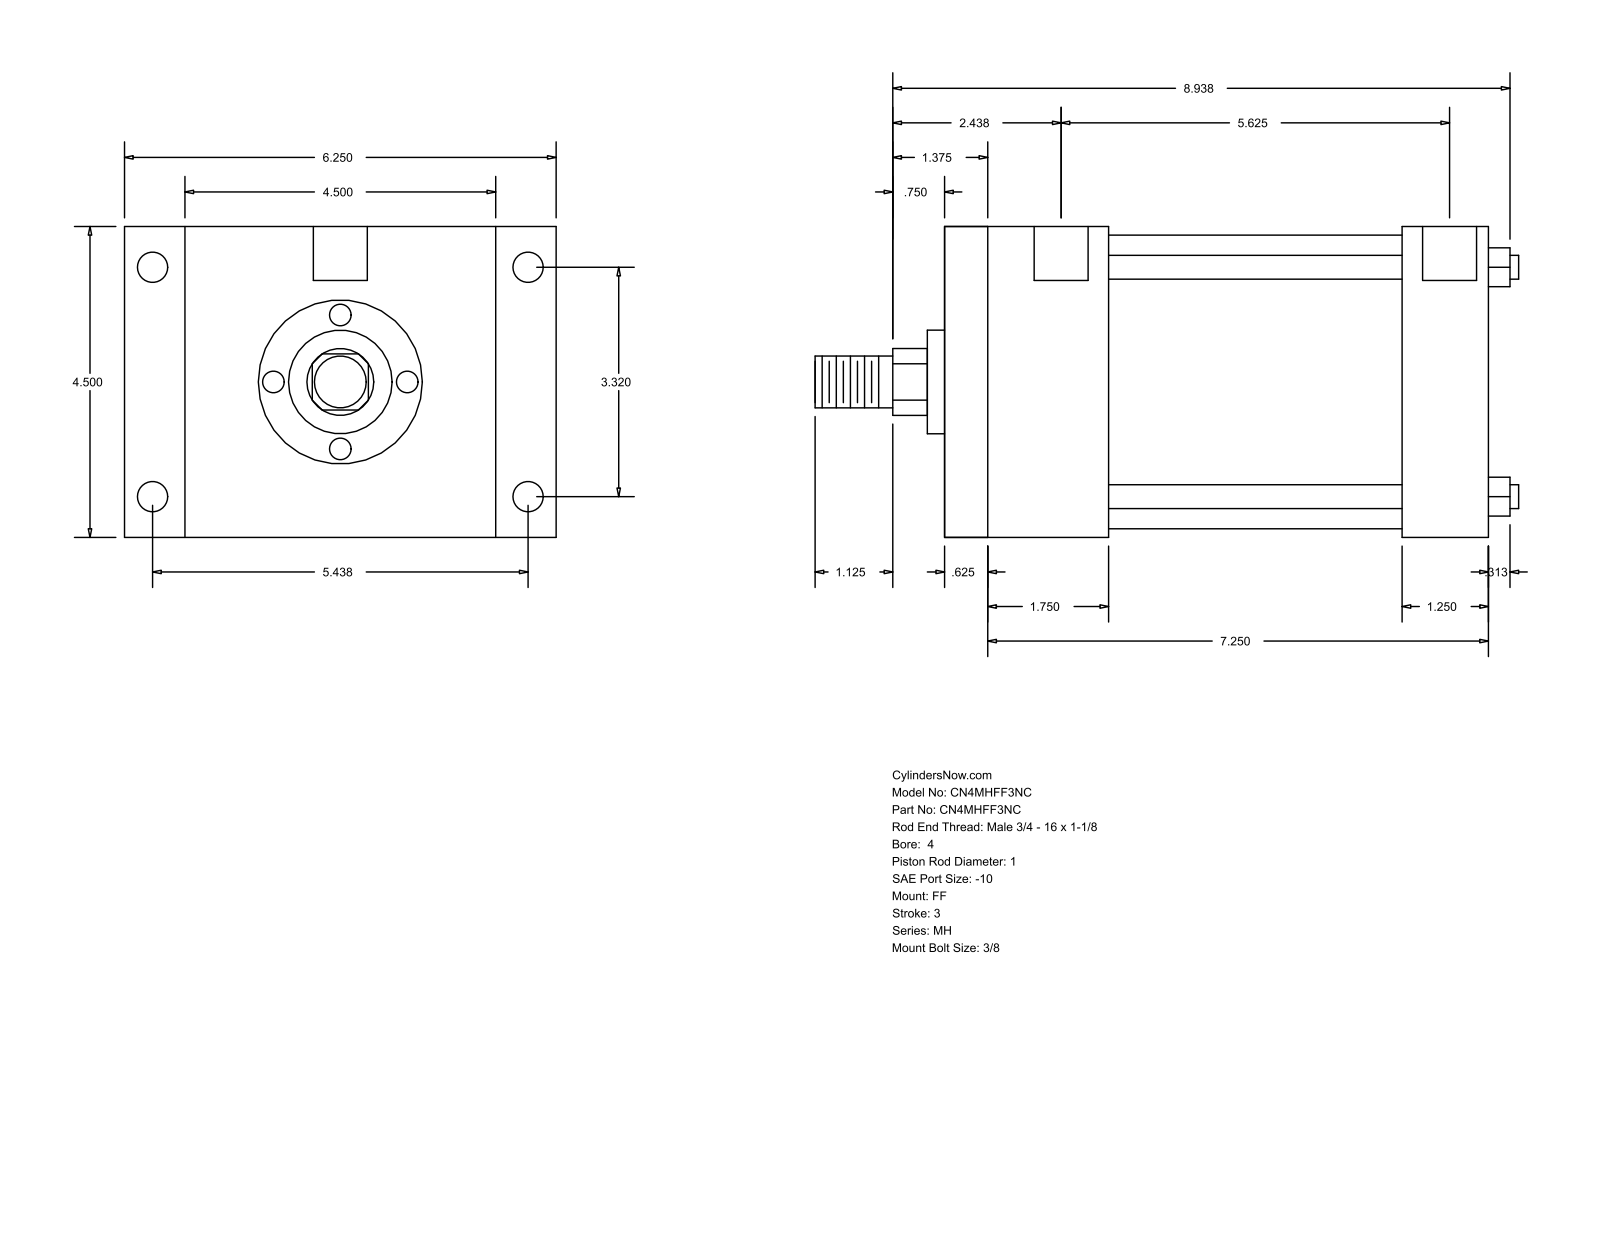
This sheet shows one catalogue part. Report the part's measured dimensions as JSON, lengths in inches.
{"part_name": "MH_FF__0400_1", "step_written_by": "GSSL Pune (CONFIG_CONTROL_DESIGN)", "units": "inches", "bodies": {"solids": 0, "faces": 92, "planar": 64, "cylindrical": 28, "other": 0}, "overall_size": [10.187, 6.25, 4.5], "round_holes": [[0.344, 4], [0.438, 4], [0.781, 2]], "round_bosses_or_shafts": [[0.345, 4], [4.25, 1], [1.5, 1], [1, 1], [0.75, 1]], "partial_cylinders_radius": [[0.484, 1]], "face_to_face_distances": [4.5, 7.875, 0.625, 7.25, 2.375, 1.75, 5.5, 6.625, 6, 4.25], "hole_center_spacings": [3.32, 5.438, 5.75, 6.371, 0.062, 0.063, 5.625, 5.687]}
